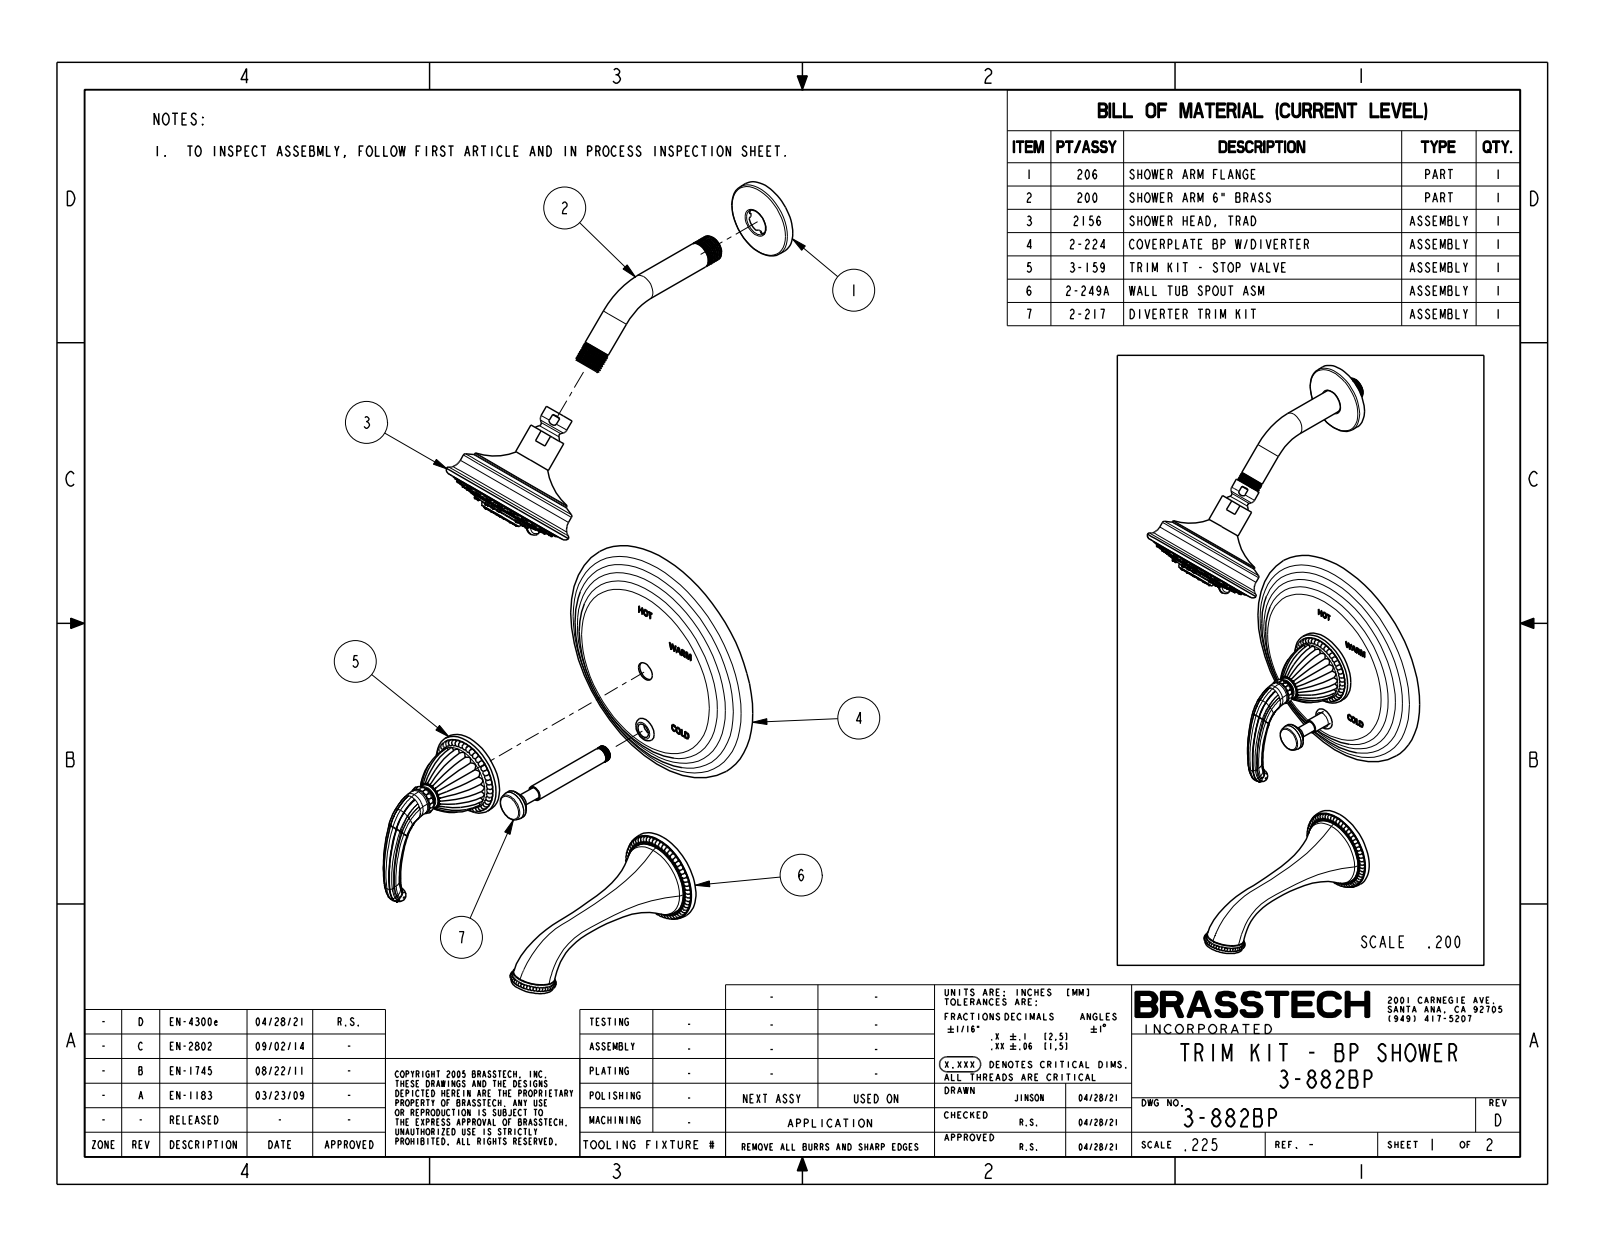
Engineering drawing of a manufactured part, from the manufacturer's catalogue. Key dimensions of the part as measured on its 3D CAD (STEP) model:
Part name (STEP PRODUCT): 3-882BP
STEP written by: CREO PARAMETRIC BY PTC INC, 2018400 (CONFIG_CONTROL_DESIGN)
Units: inches
Bodies: 3 solids, 2109 faces (353 planar, 216 cylindrical, 1540 other)
Overall size (bounding box): 21.615 × 8.25 × 7.75
Volume: 62.26 in³ · Surface area: 231.3 in²
Round holes (diameter × count): ⌀0.059 ×8, ⌀0.925 ×1
Round bosses / shafts (diameter × count): ⌀0.142 ×39, ⌀0.165 ×23, ⌀0.813 ×2, ⌀3.81 ×1, ⌀3.724 ×1, ⌀3.24 ×1, ⌀2.57 ×1, ⌀2.435 ×1
Partial cylindrical surfaces — rounded edges, fillets, slot ends (radius × count): R0.079 ×8, R0.02 ×2, R0.138 ×1, R0.472 ×1, R0.512 ×1, R0.63 ×1
Main face-to-face distances: 0.754, 0.063, 0.118, 0.181, 2.495, 1.741, 0.29, 0.464, 2.205, 2.881
Hole centre spacings: 0.443, 0.579, 1.069, 0.819, 0.818, 1.157, 1.157
